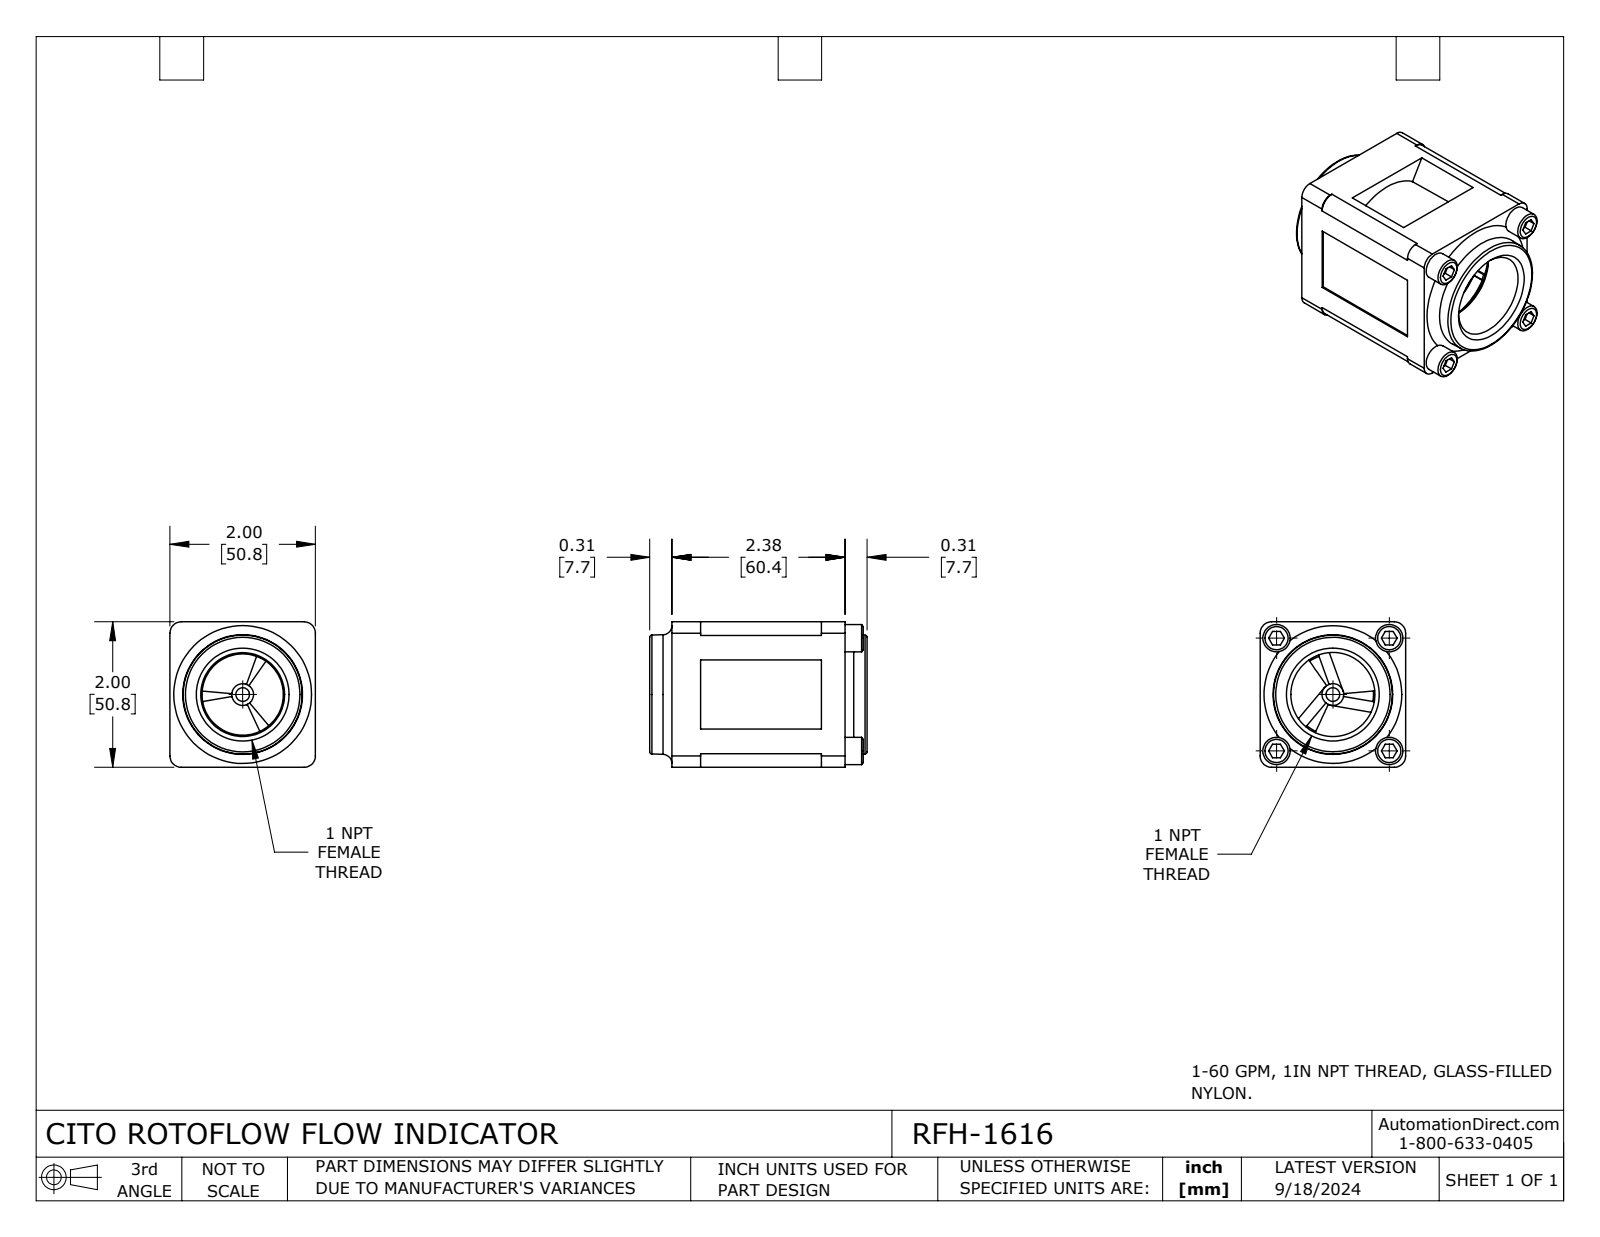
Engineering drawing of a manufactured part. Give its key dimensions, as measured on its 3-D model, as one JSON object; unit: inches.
{"part_name": "RFH-1616", "step_written_by": "SolidWorks 2023 (CONFIG_CONTROL_DESIGN)", "units": "inches", "bodies": {"solids": 3, "faces": 222, "planar": 101, "cylindrical": 70, "other": 51}, "overall_size": [2.99, 2, 2], "volume_in3": 5.868, "surface_area_in2": 69.87, "round_holes": [[0.201, 4], [0.257, 4], [0.187, 1], [0.3, 1], [1.156, 1], [1.45, 1]], "round_bosses_or_shafts": [[0.375, 4]], "partial_cylinders_radius": [[0.156, 4], [0.187, 4], [0.046, 3]], "face_to_face_distances": [2, 0.02, 1.98, 1.96, 0.7, 2.289, 0.395, 1.984, 2.38, 0.395], "hole_center_spacings": [1.096, 1.55, 2.191]}
